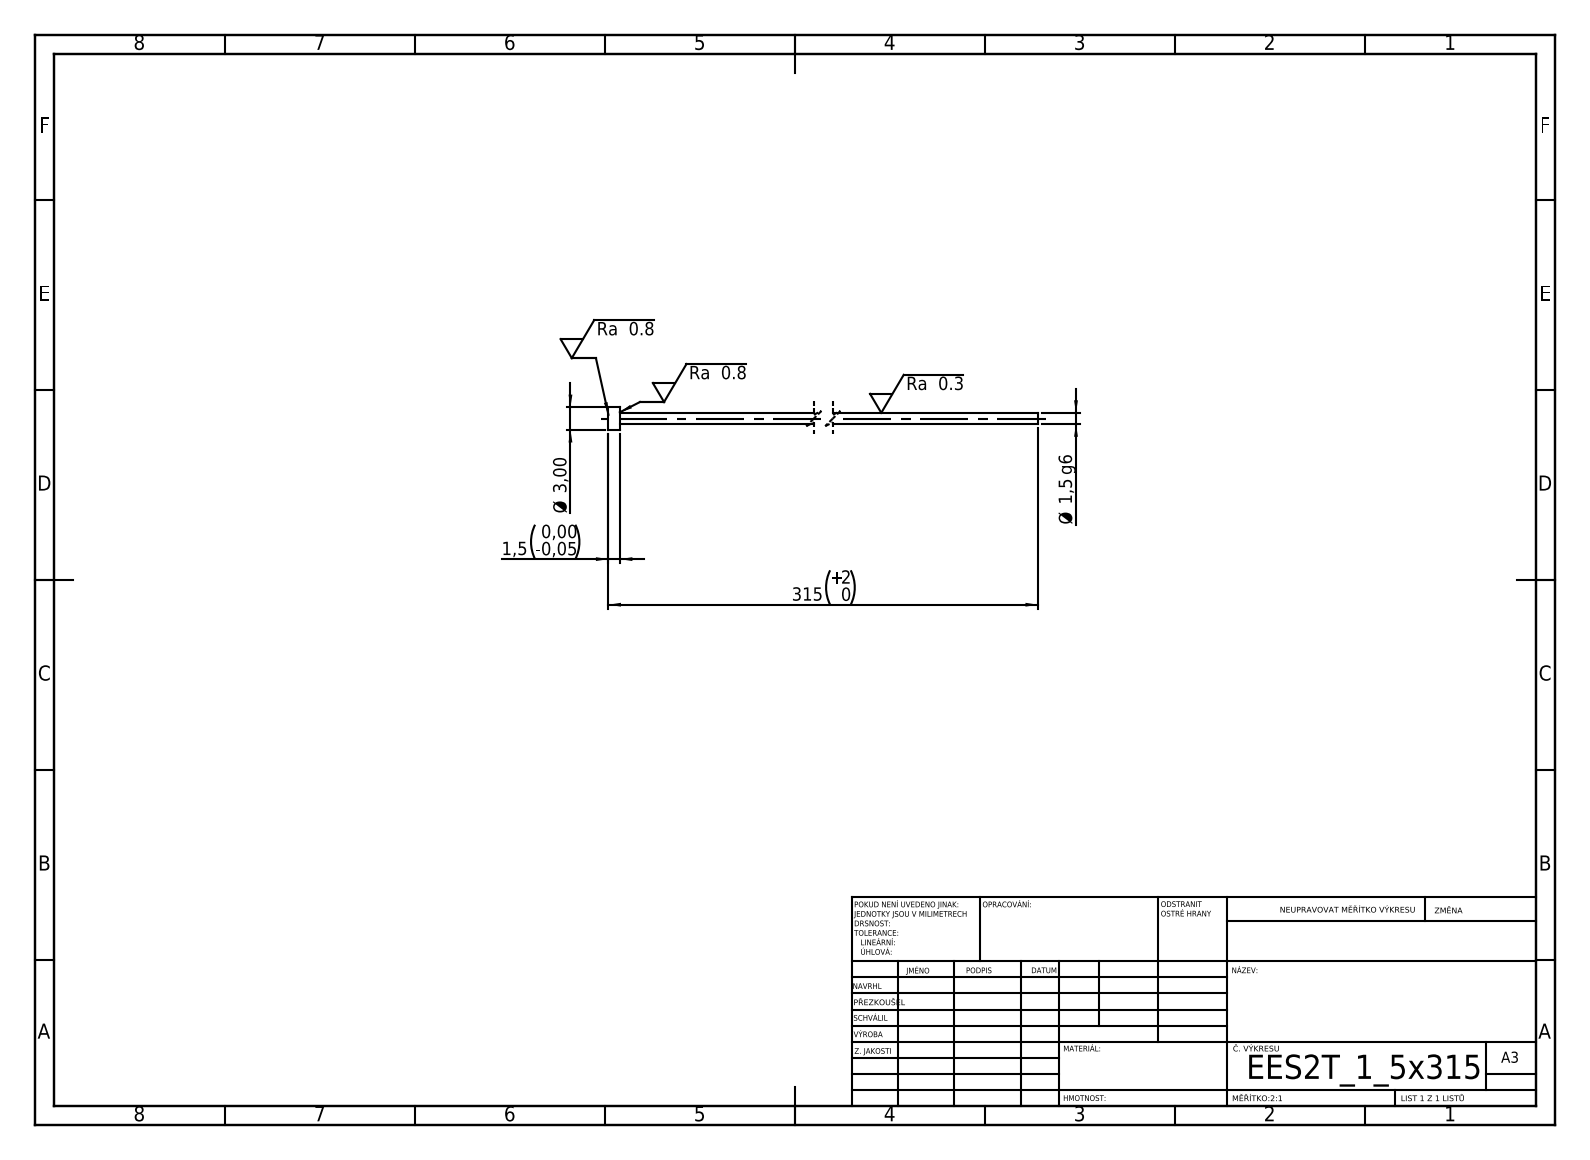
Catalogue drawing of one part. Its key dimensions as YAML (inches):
step_written_by: "SolidWorks 2019 (CONFIG_CONTROL_DESIGN)"
units: inches
bodies: {solids: 1, faces: 7, planar: 3, cylindrical: 4, other: 0}
overall_size: [12.402, 0.118, 0.118]
volume: 0.034
surface_area: 2.334
round_bosses_or_shafts:
  - {diameter: 0.118, count: 1}
  - {diameter: 0.059, count: 1}
face_to_face_distances: [0.059, 12.402, 12.343]
